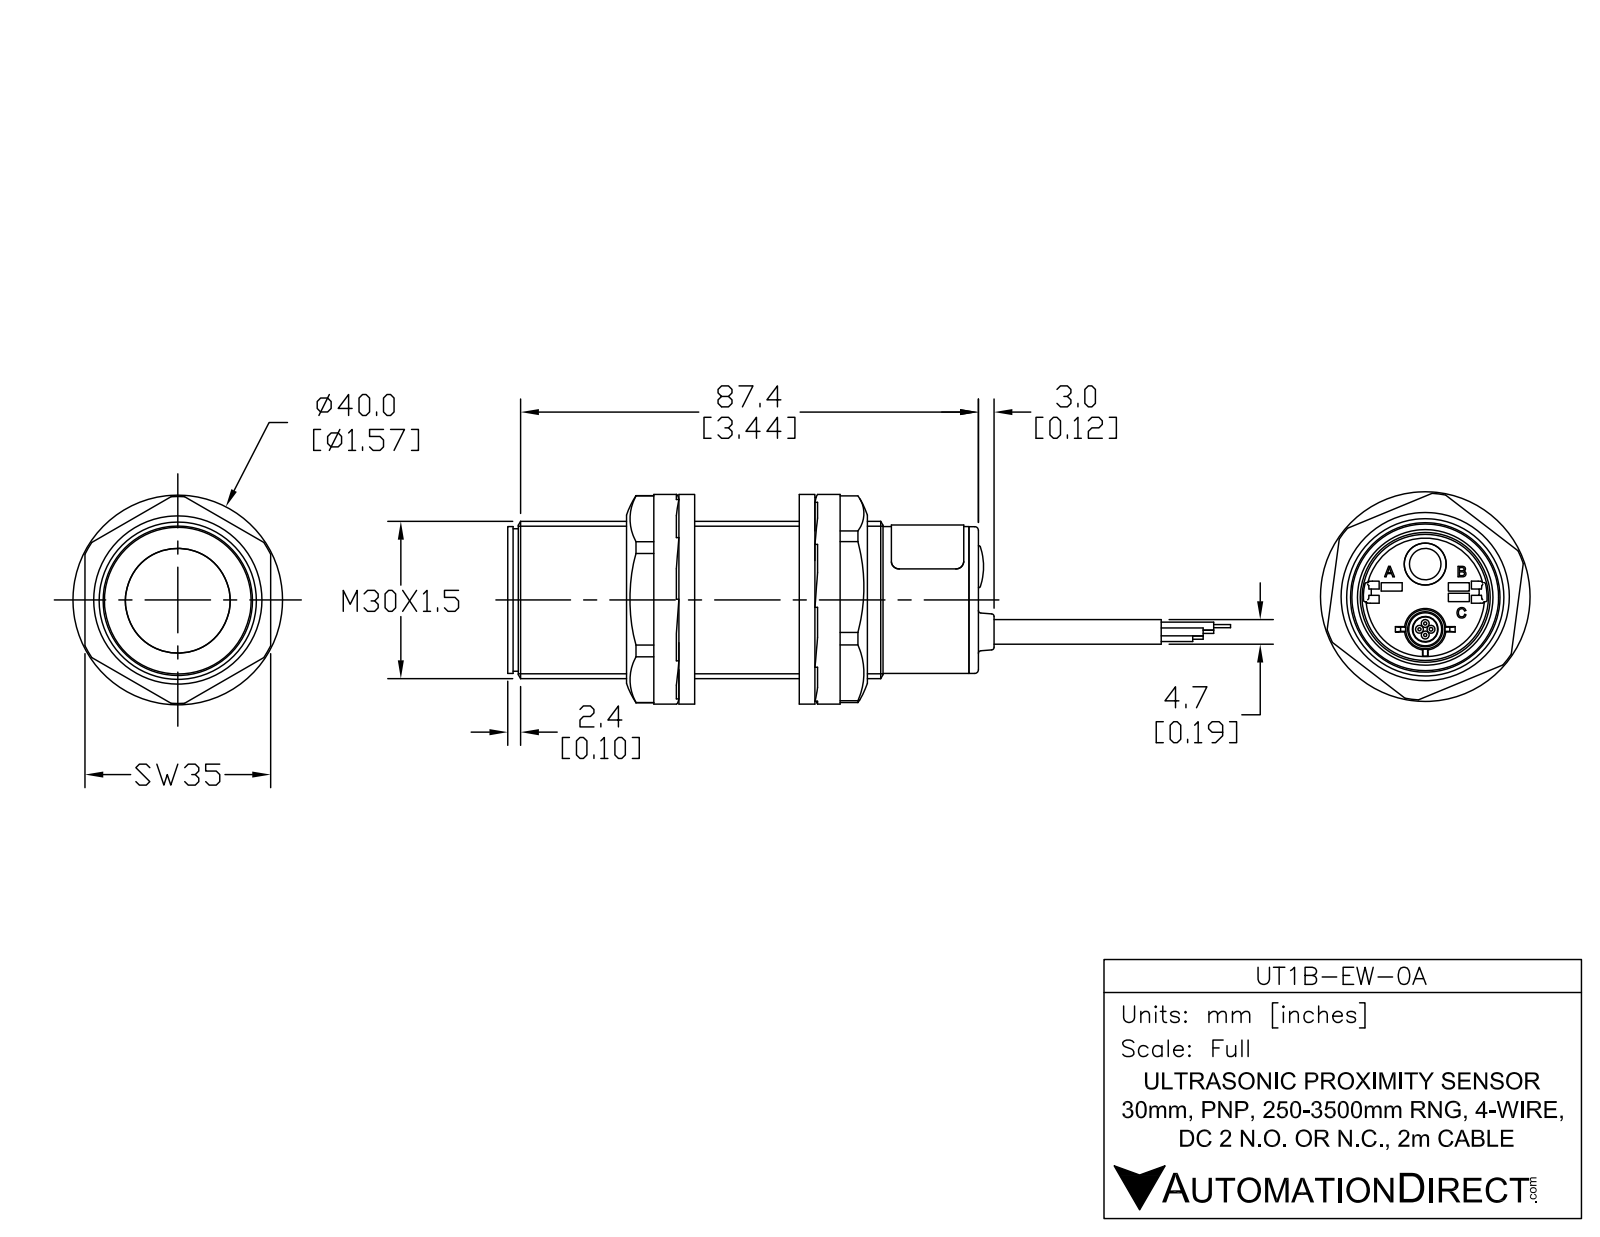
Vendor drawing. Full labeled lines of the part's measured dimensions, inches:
Part name (STEP PRODUCT): UT1B-EW-0A
STEP written by: SolidWorks 2017 (AUTOMOTIVE_DESIGN)
Units: inches
Bodies: 5 solids, 48 faces (13 planar, 18 cylindrical, 17 other)
Overall size (bounding box): 5.039 × 1.181 × 1.181
Volume: 3.762 in³ · Surface area: 19.85 in²
Round holes (diameter × count): ⌀0.185 ×1, ⌀0.315 ×1, ⌀0.925 ×1
Round bosses / shafts (diameter × count): ⌀1.181 ×1, ⌀1.102 ×1, ⌀1.071 ×1
Main face-to-face distances: 3.386, 3.457, 0.071, 0.039, 3.425, 3.496, 0.039, 3.425, 3.496, 0.031
Hole centre spacings: 0.239, 0.25, 0.49
